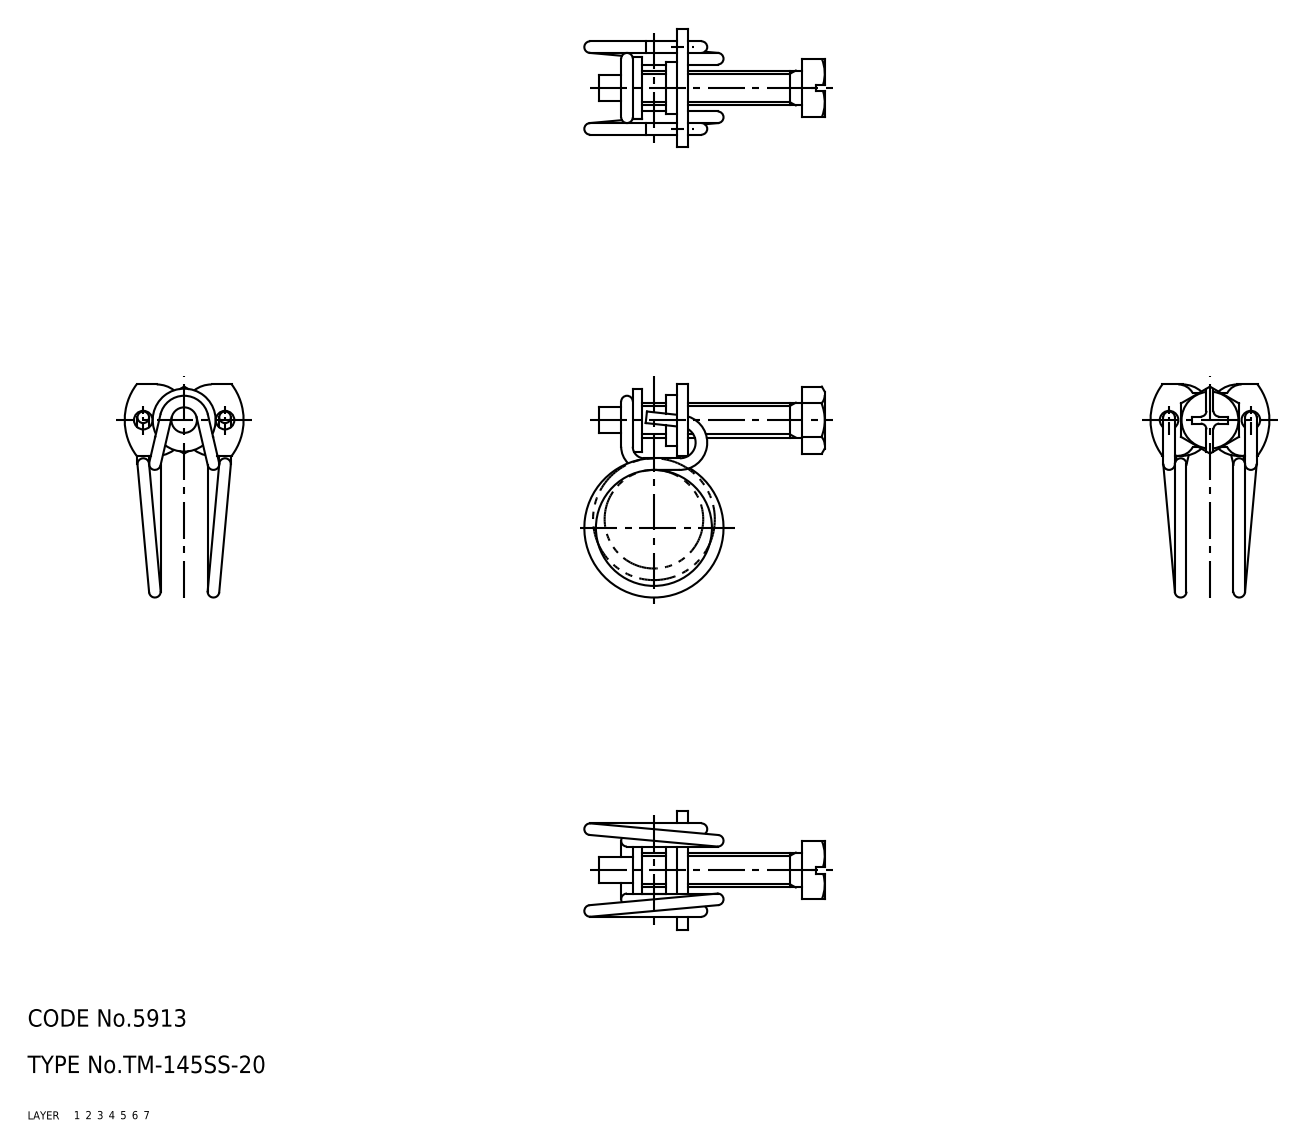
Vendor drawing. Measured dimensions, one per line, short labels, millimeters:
name: 67116278; 67116291; 67116304
written by: CADfix (AUTOMOTIVE_DESIGN)
unit: mm
bodies: 3 solids, 98 faces (0 planar, 0 cylindrical, 98 other)
size: 41.45 × 36.74 × 20.5
volume: 2 424 mm³; area: 3 132 mm²
